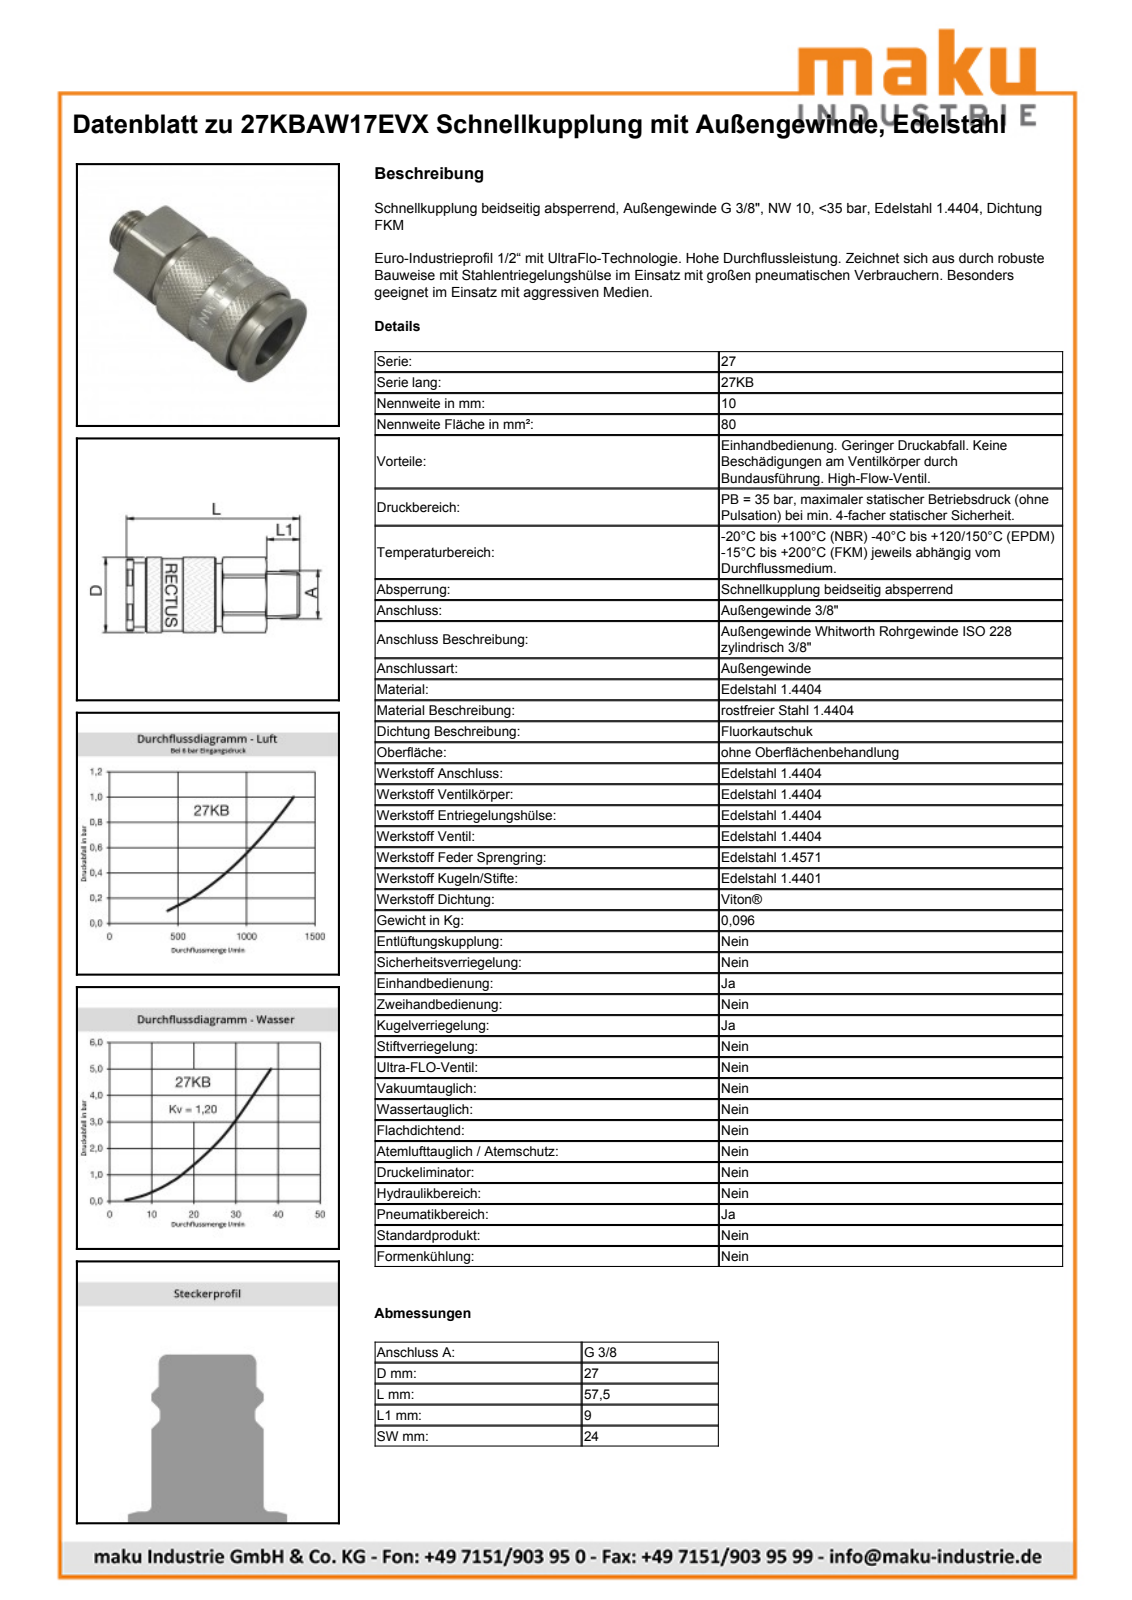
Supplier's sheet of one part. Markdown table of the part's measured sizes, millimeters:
| quantity | value |
| --- | --- |
| part name | D104153 |
| STEP written by | Autodesk Inventor 2013 (AUTOMOTIVE_DESIGN) |
| units | millimeters |
| bodies | 2 solids, 742 faces (322 planar, 82 cylindrical, 338 other) |
| overall size | 57.45 × 27.15 × 27.15 |
| volume | 25 196 mm³ |
| surface area | 10 391 mm² |
| round holes (diameter × count) | 19 × 1, 20.3 × 1, 20.95 × 1, 23.35 × 1, 23.55 × 1 |
| round bosses / shafts (diameter × count) | 27.15 × 1, 26 × 1, 23.1 × 1, 22.8 × 1, 20 × 1, 18.77 × 1, 16.66 × 1 |
| partial cylindrical surfaces (radius × count) | 12.9 × 1, 13.53 × 1 |
| main face-to-face distances | 24, 57.45, 48.45, 9, 31.75, 16.7, 25.7, 6.25, 25.5, 42.2 |
